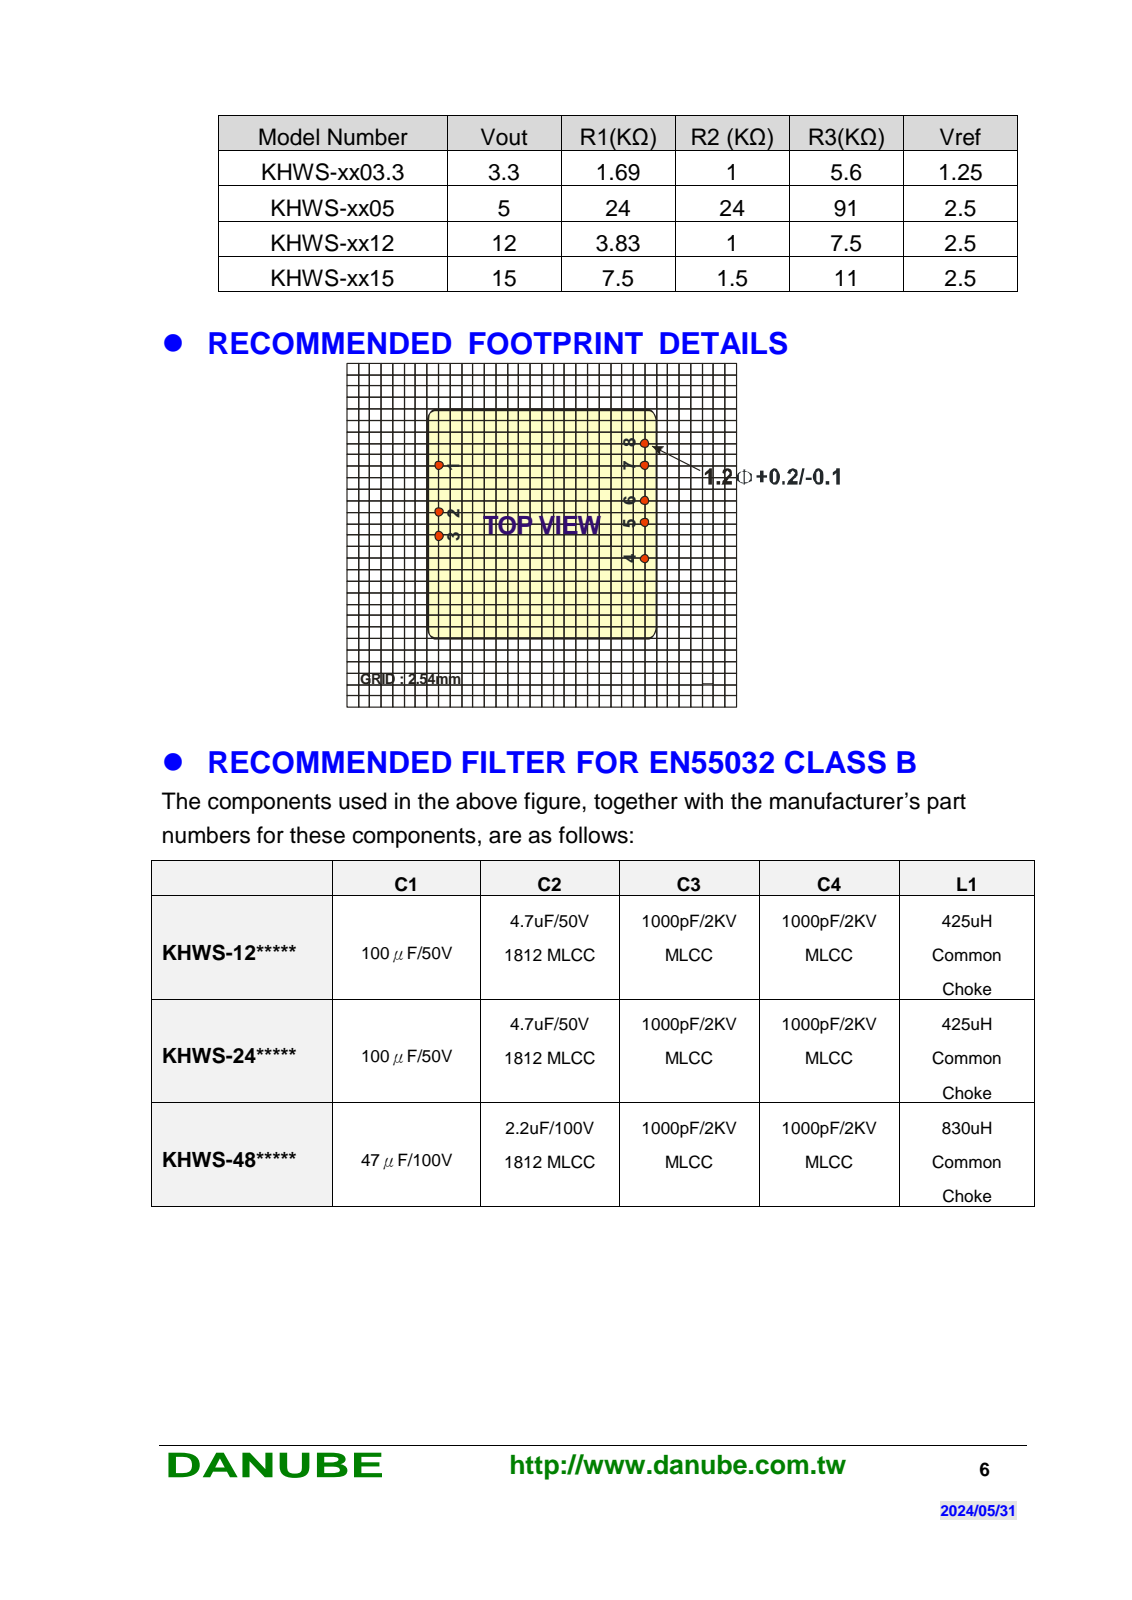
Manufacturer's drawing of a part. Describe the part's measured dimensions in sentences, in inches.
The part is named "case; pin_2; pin_1; pin_3 (+5 more)". Its 3-D file was written by "FreeCAD (AUTOMOTIVE_DESIGN)". It is 9 solids with 42 faces: 22 planar, 16 cylindrical and 4 other. Overall it measures 2 by 2 by 0.661 inches. Its volume is 1.722 cubic inches and its surface area 11.37 square inches. Round bosses or shafts: 8 of diameter 0.039. Partial cylindrical surfaces (rounded edges, fillets, slot ends): 8 of radius 0.079. The main face-to-face distances are 0.433, 2, 0.228, 0.661.
